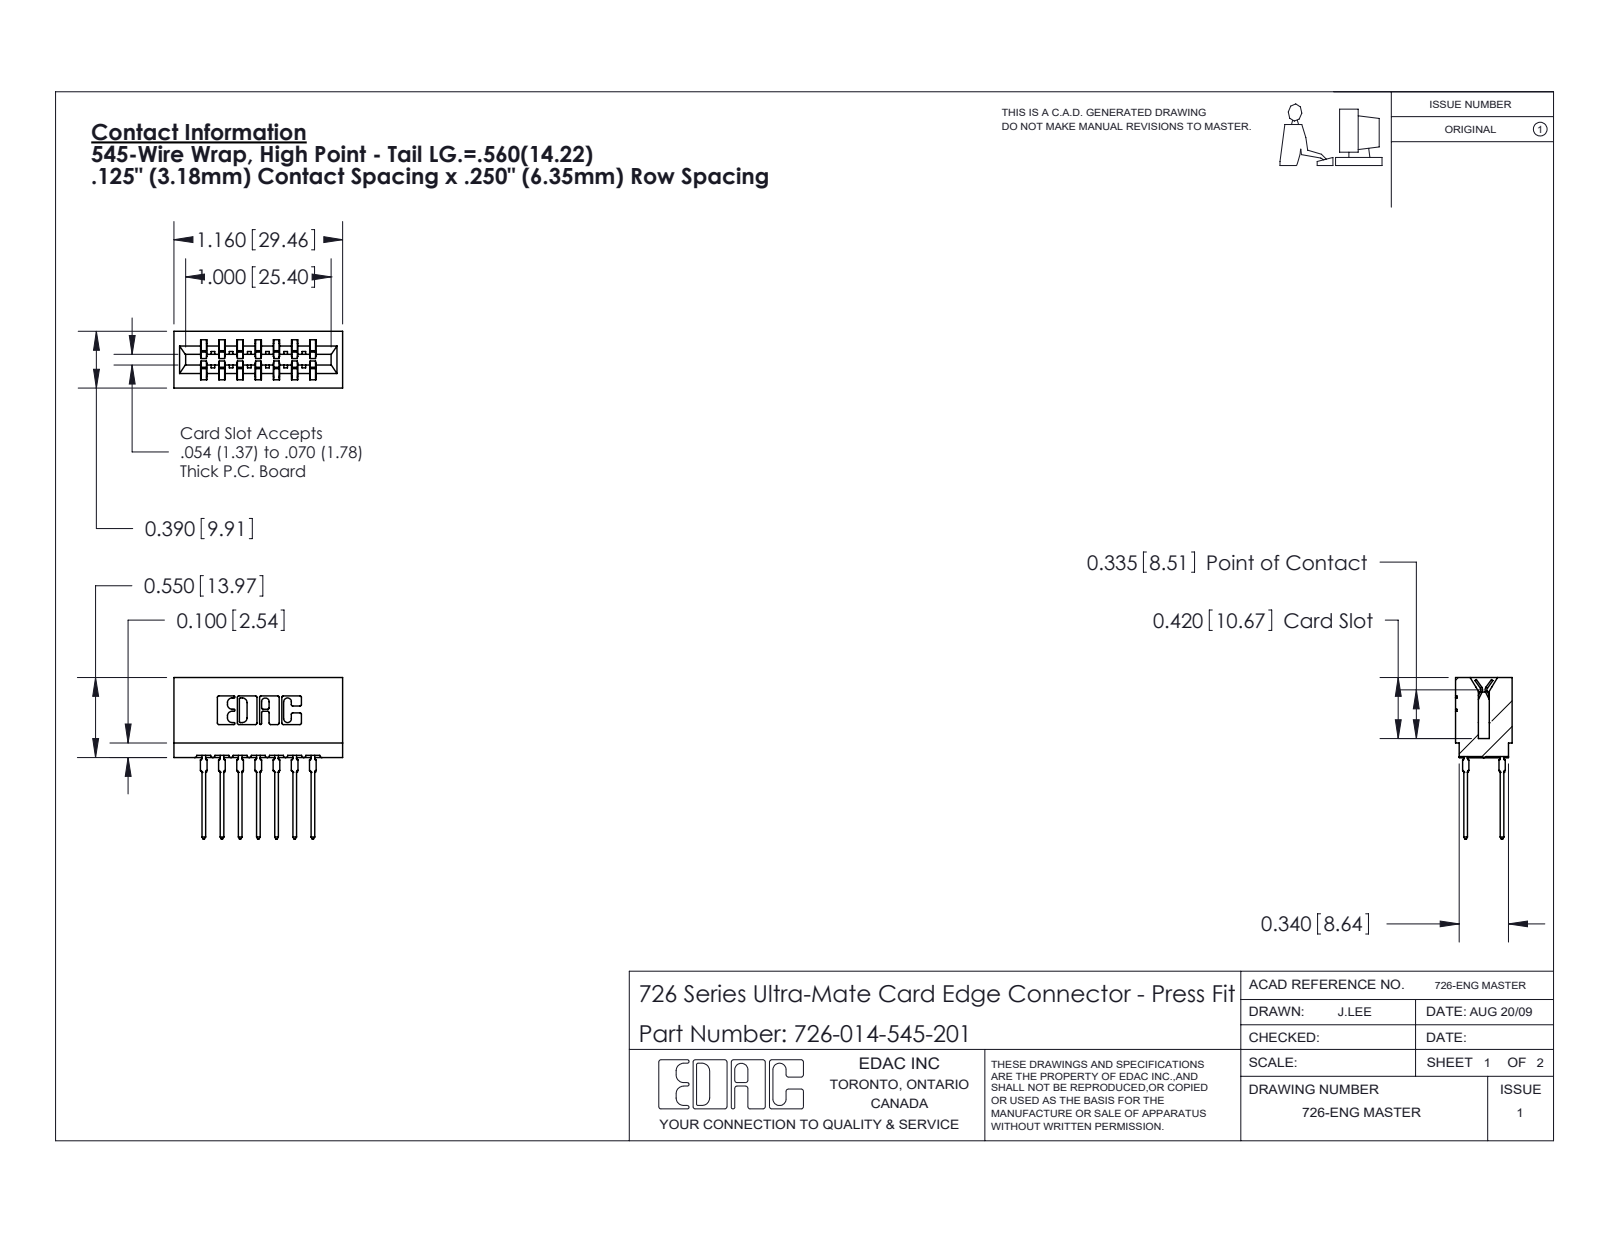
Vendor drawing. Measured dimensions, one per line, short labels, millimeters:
name: 726 Part_.515 Slot Depth - 01; 726-014-545-201; 746-292-001_545
written by: SolidWorks 2020 (CONFIG_CONTROL_DESIGN)
unit: mm
bodies: 15 solids, 1350 faces (699 planar, 287 cylindrical, 364 other)
size: 29.5 × 28.2 × 9.9
volume: 2 950 mm³; area: 4 510 mm²
rounds: 28× R0.5, 22× R0.3, 8× R0.1, 8× R0.3, 8× R0.4, 6× R0.2, 6× R0.8, 3× R0.7
face distances: 6.4, 1.4, 8.5, 1.1, 3.2, 3.2, 2.1, 12.7, 0.6, 7.8
